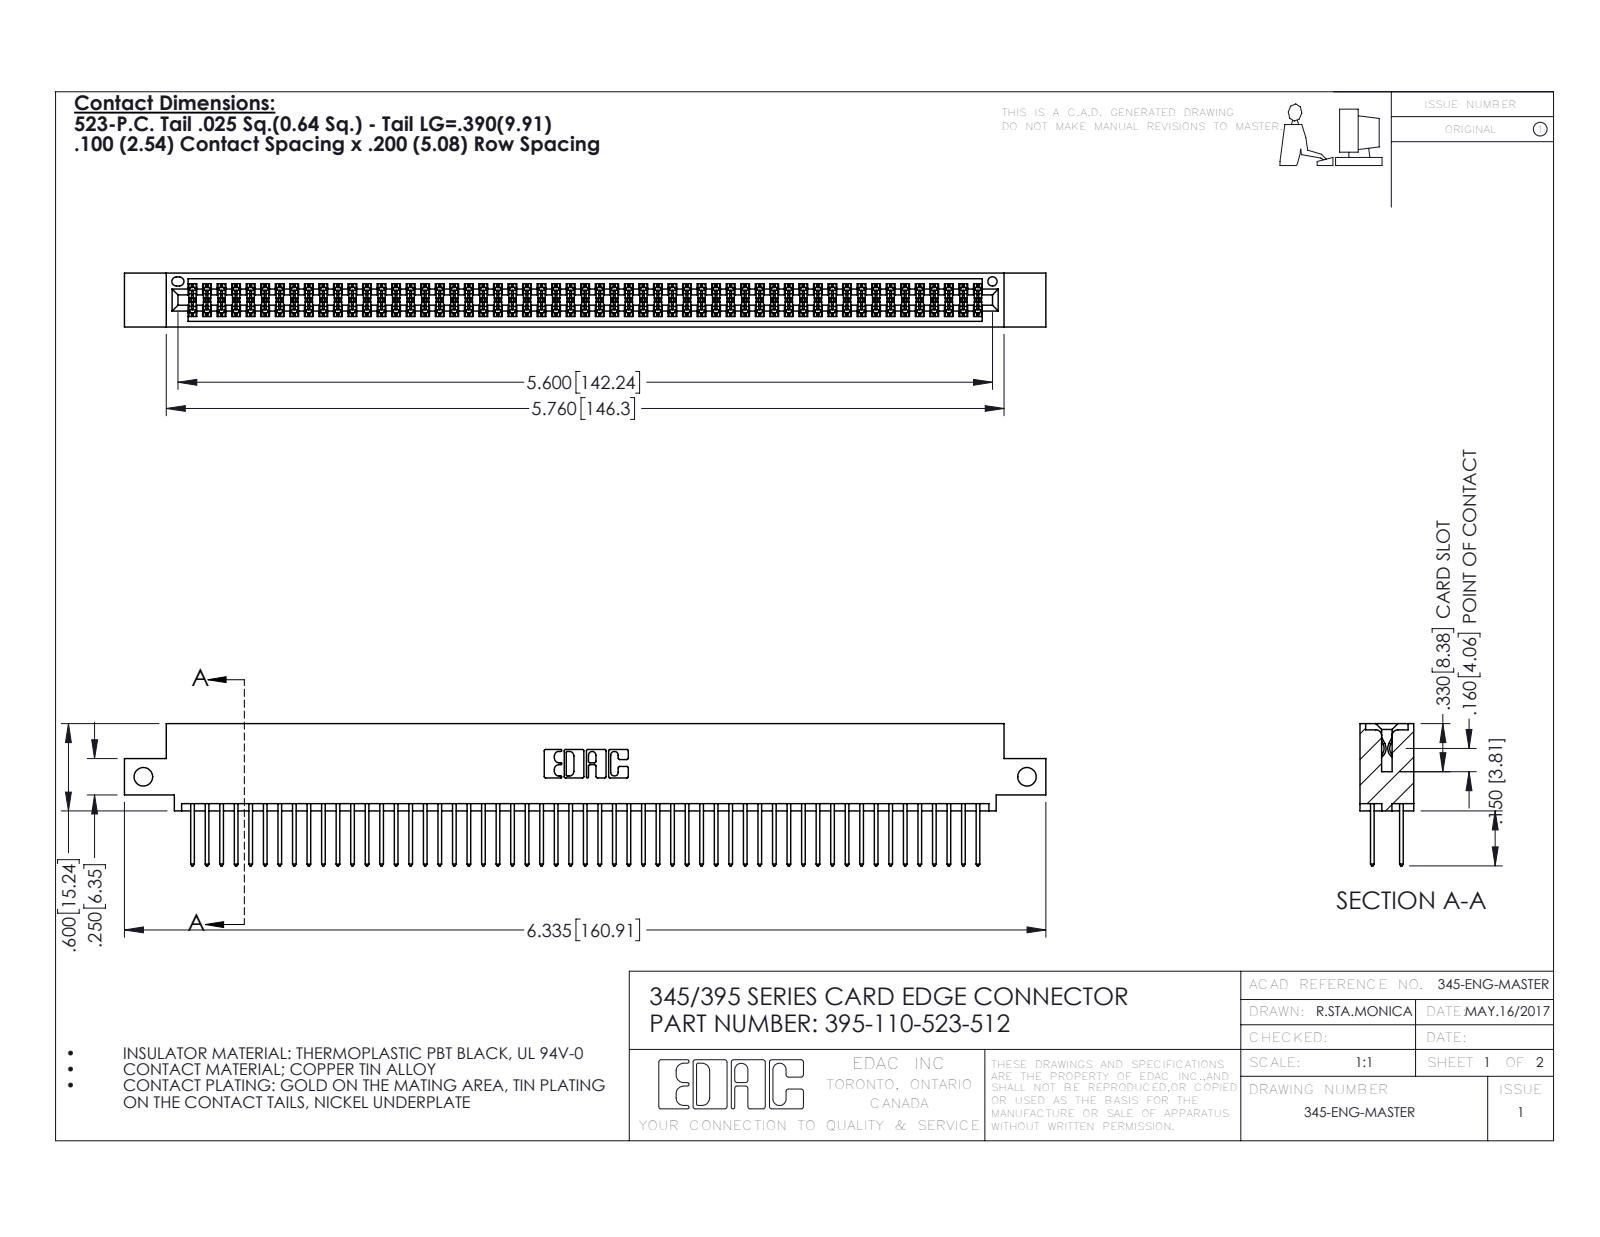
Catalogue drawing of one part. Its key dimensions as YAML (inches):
part_name: "345 Part_0.110 Offset - Side Mount; 345-292-001_345-293-123; 395-110-523-512"
step_written_by: "SolidWorks 2016 (CONFIG_CONTROL_DESIGN)"
units: inches
bodies: {solids: 111, faces: 5630, planar: 3714, cylindrical: 1916, other: 0}
overall_size: [6.335, 0.977, 0.37]
volume: 0.965
surface_area: 38.13
round_holes:
  - {diameter: 0.128, count: 2}
  - {diameter: 0.064, count: 1}
partial_cylinders:
  - {radius: 0.006, count: 165}
  - {radius: 0.01, count: 110}
  - {radius: 0.01, count: 22}
  - {radius: 0.007, count: 6}
  - {radius: 0.031, count: 6}
  - {radius: 0.026, count: 3}
  - {radius: 0.014, count: 2}
  - {radius: 0.019, count: 2}
face_to_face_distances: [0.072, 0.298, 0.2, 0.098, 0.272, 0.025, 0.37, 0.225, 0.175, 0.149]
hole_center_spacings: [6.075]
